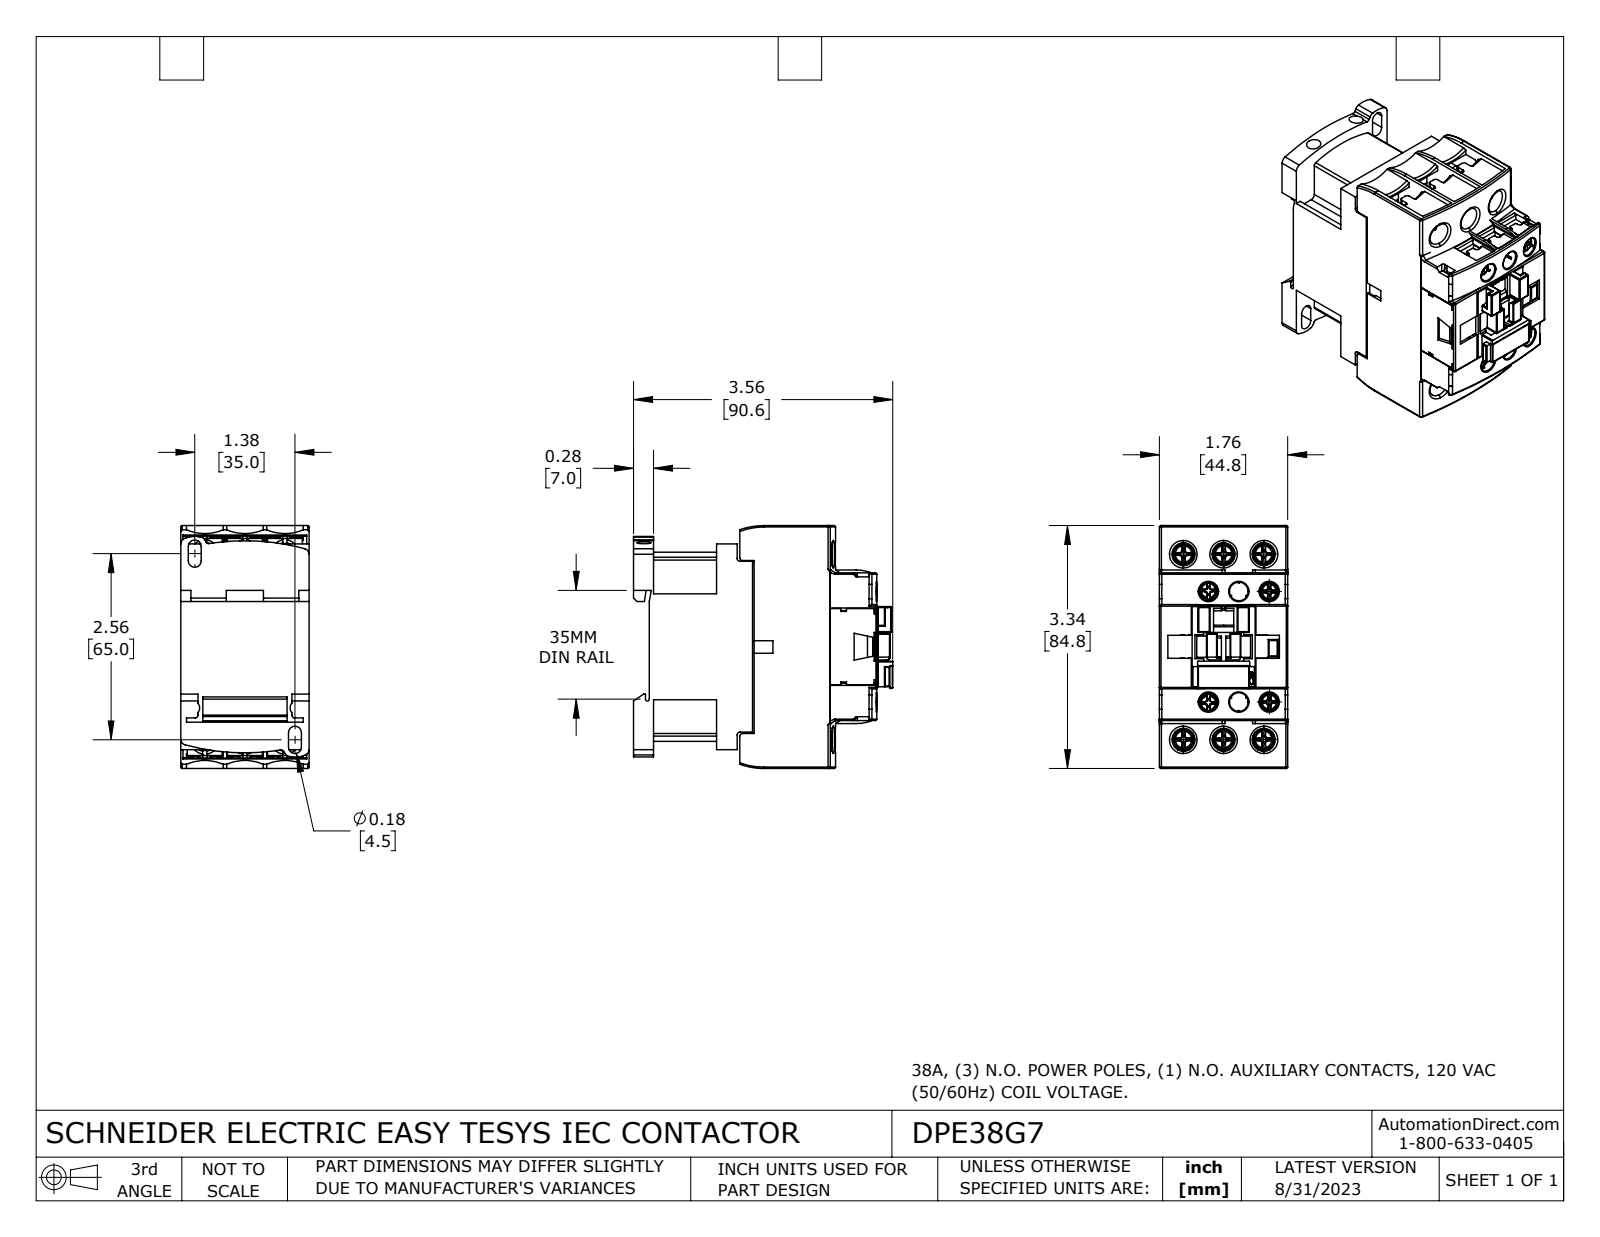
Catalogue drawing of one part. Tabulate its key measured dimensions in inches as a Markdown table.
| quantity | value |
| --- | --- |
| part name | DPE38G7 |
| STEP written by | SolidWorks 2021 (CONFIG_CONTROL_DESIGN) |
| units | inches |
| bodies | 16 solids, 2674 faces (1724 planar, 584 cylindrical, 366 other) |
| overall size | 3.565 × 3.339 × 1.764 |
| volume | 12.56 in³ |
| surface area | 100.4 in² |
| round holes (diameter × count) | 0.256 × 6, 0.315 × 6, 0.197 × 2 |
| round bosses / shafts (diameter × count) | 0.157 × 8, 0.126 × 6, 0.138 × 4, 0.134 × 4, 0.108 × 4, 0.394 × 3 |
| partial cylindrical surfaces (radius × count) | 0.012 × 58, 0.006 × 36, 0.039 × 36, 0.02 × 34, 0.63 × 18, 0.008 × 17, 0.079 × 9, 0.031 × 8 |
| main face-to-face distances | 1.764, 0.551, 0.022, 0.059, 1.089, 1.067, 0.047, 0.031, 1.382, 1.419 |
| hole center spacings | 0.417, 0.551, 1.576, 2.61, 1.52, 2.551, 0.553, 0.56 |
